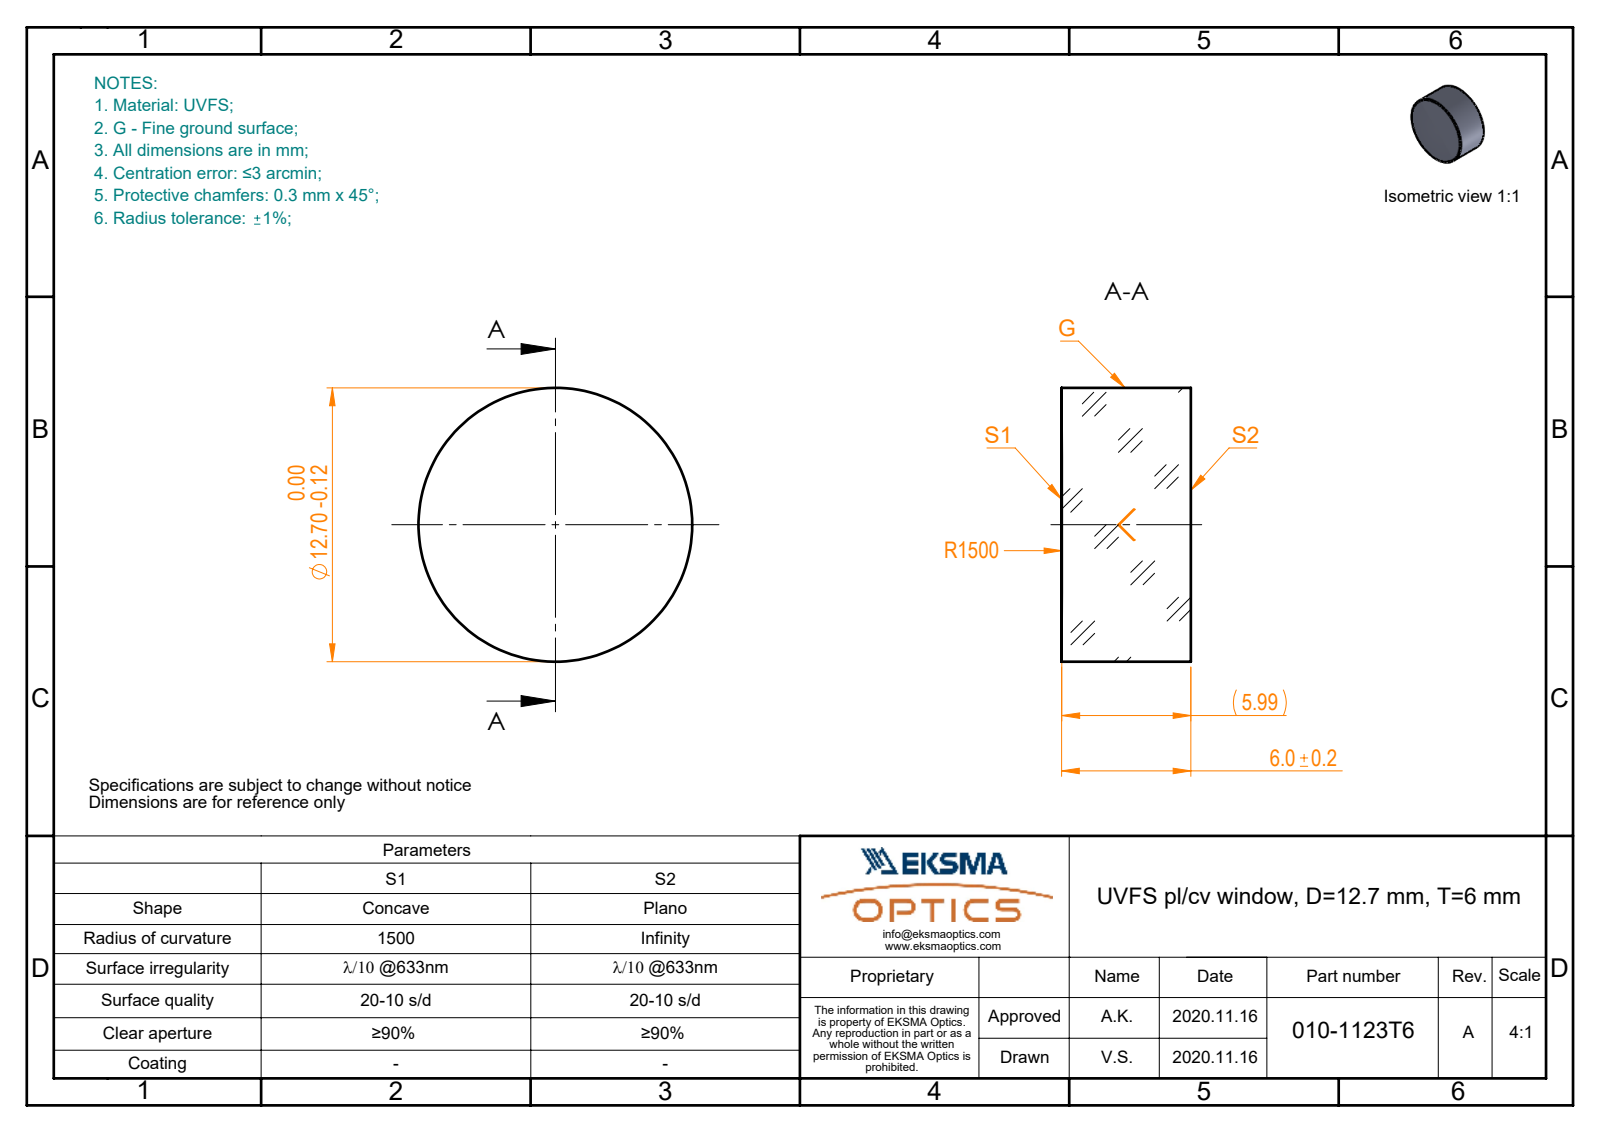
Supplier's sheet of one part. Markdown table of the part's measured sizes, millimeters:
| quantity | value |
| --- | --- |
| part name | 010-1123T6_UVFS_PCV_window |
| STEP written by | SolidWorks 2019 (CONFIG_CONTROL_DESIGN) |
| units | millimeters |
| bodies | 1 solid, 5 faces (1 planar, 2 cylindrical, 2 other) |
| overall size | 12.7 × 12.7 × 6 |
| volume | 759 mm³ |
| surface area | 493 mm² |
| round bosses / shafts (diameter × count) | 12.7 × 1 |
